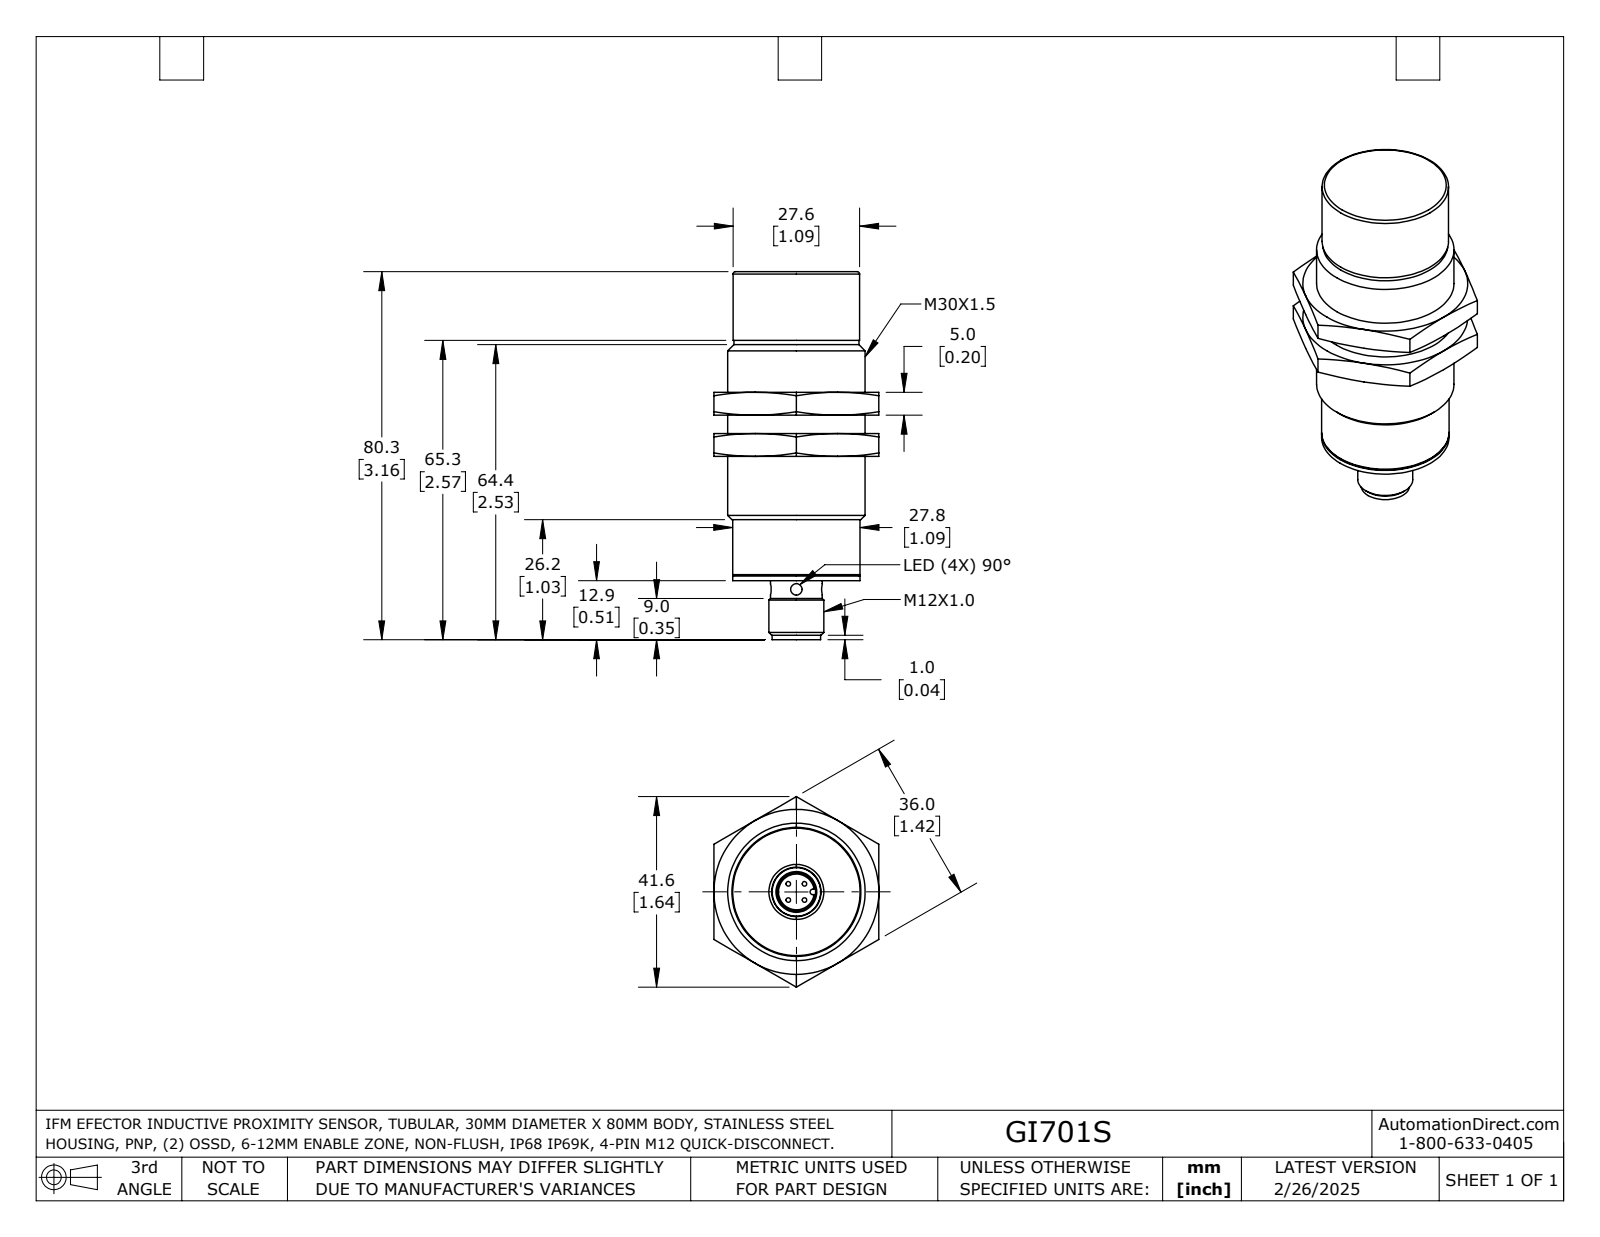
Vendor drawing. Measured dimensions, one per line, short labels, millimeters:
name: GI701S
written by: SolidWorks 2024 (AUTOMOTIVE_DESIGN)
unit: mm
bodies: 3 solids, 120 faces (27 planar, 37 cylindrical, 56 other)
size: 80.3 × 41.57 × 36
volume: 50 002 mm³; area: 12 021 mm²
holes: 2× ⌀2.5, 1× ⌀8.4, 1× ⌀28.38
bosses: 1× ⌀30, 1× ⌀27.8, 1× ⌀27.6, 1× ⌀27.3, 1× ⌀12, 1× ⌀11.3, 1× ⌀10.6
rounds: 1× R0.6, 1× R4.7
face distances: 5, 9, 67.4, 36, 4, 36.1, 26.3, 35.3, 41.1, 32.1
